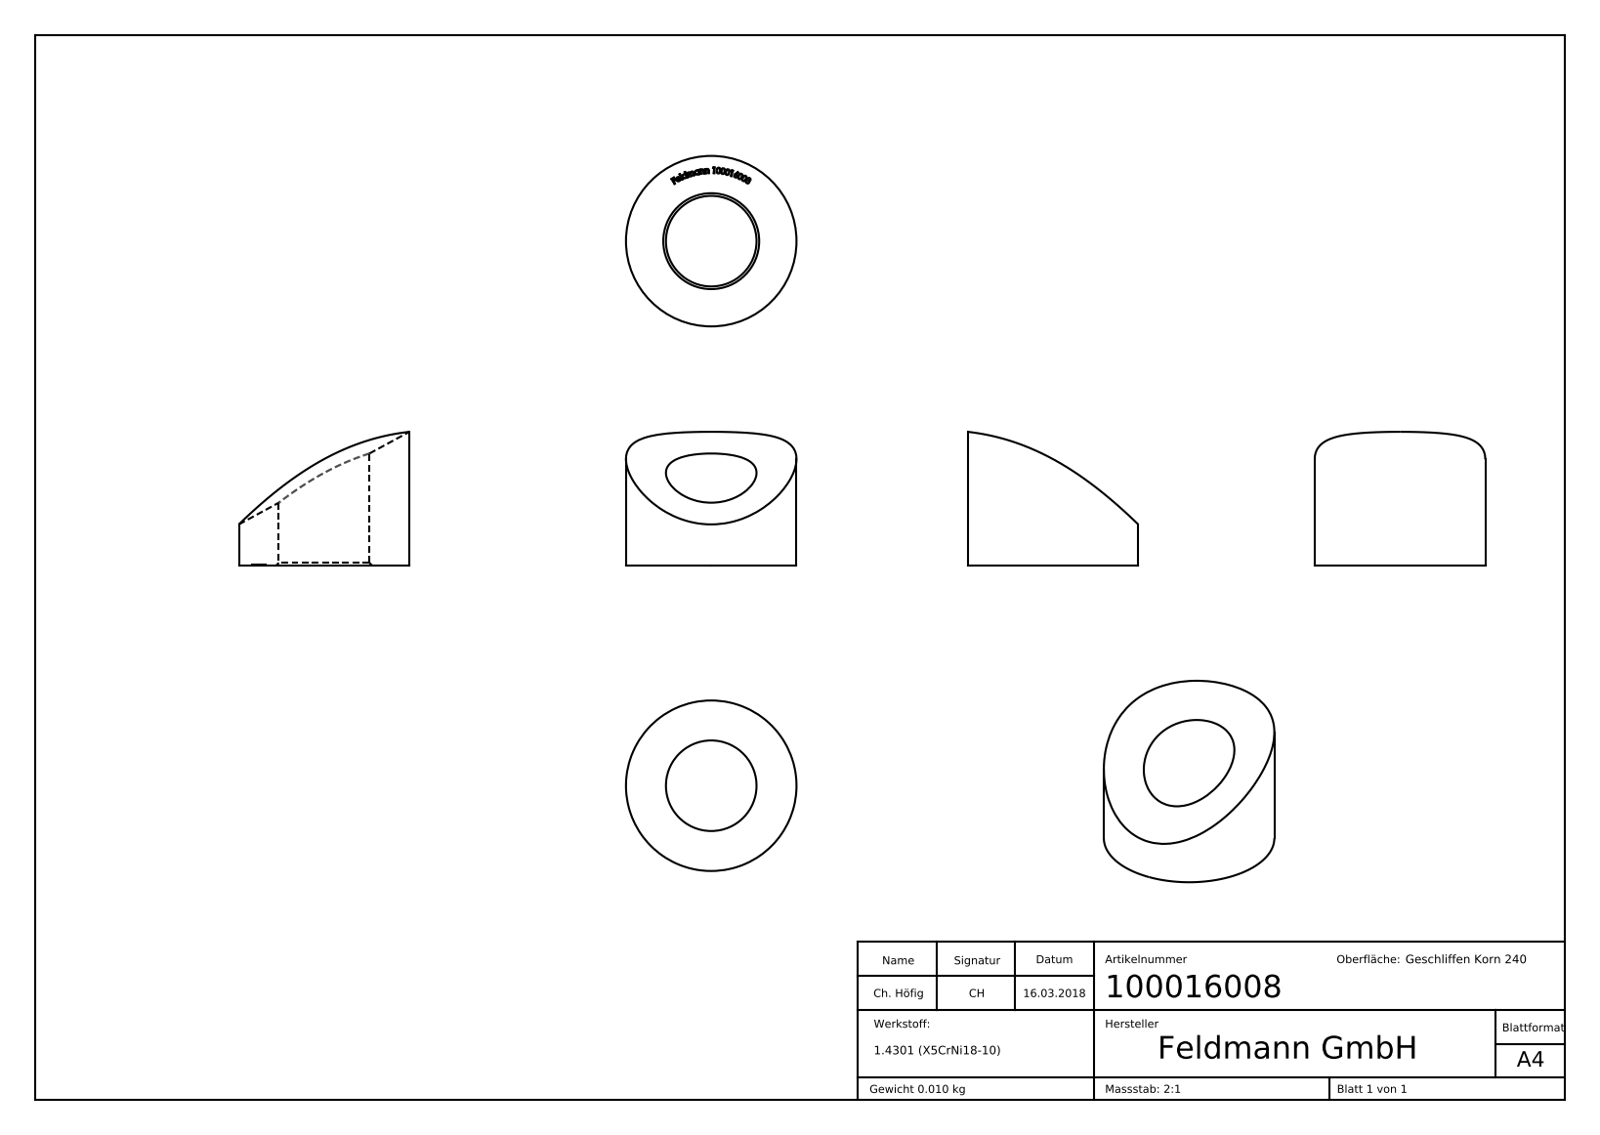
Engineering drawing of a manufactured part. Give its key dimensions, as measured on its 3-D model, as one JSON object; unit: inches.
{"part_name": "100016008", "step_written_by": "SolidWorks 2015 (CONFIG_CONTROL_DESIGN)", "units": "inches", "bodies": {"solids": 1, "faces": 224, "planar": 98, "cylindrical": 5, "other": 121}, "overall_size": [0.63, 0.63, 0.494], "volume_in3": 0.077, "surface_area_in2": 1.54, "round_holes": [[0.335, 1]], "round_bosses_or_shafts": [[0.63, 1]], "partial_cylinders_radius": [[0.835, 1]], "face_to_face_distances": [0.021, 0.013, 0.023, 0.019, 0.015, 0.013, 0.012, 0.021, 0.019, 0.02]}
